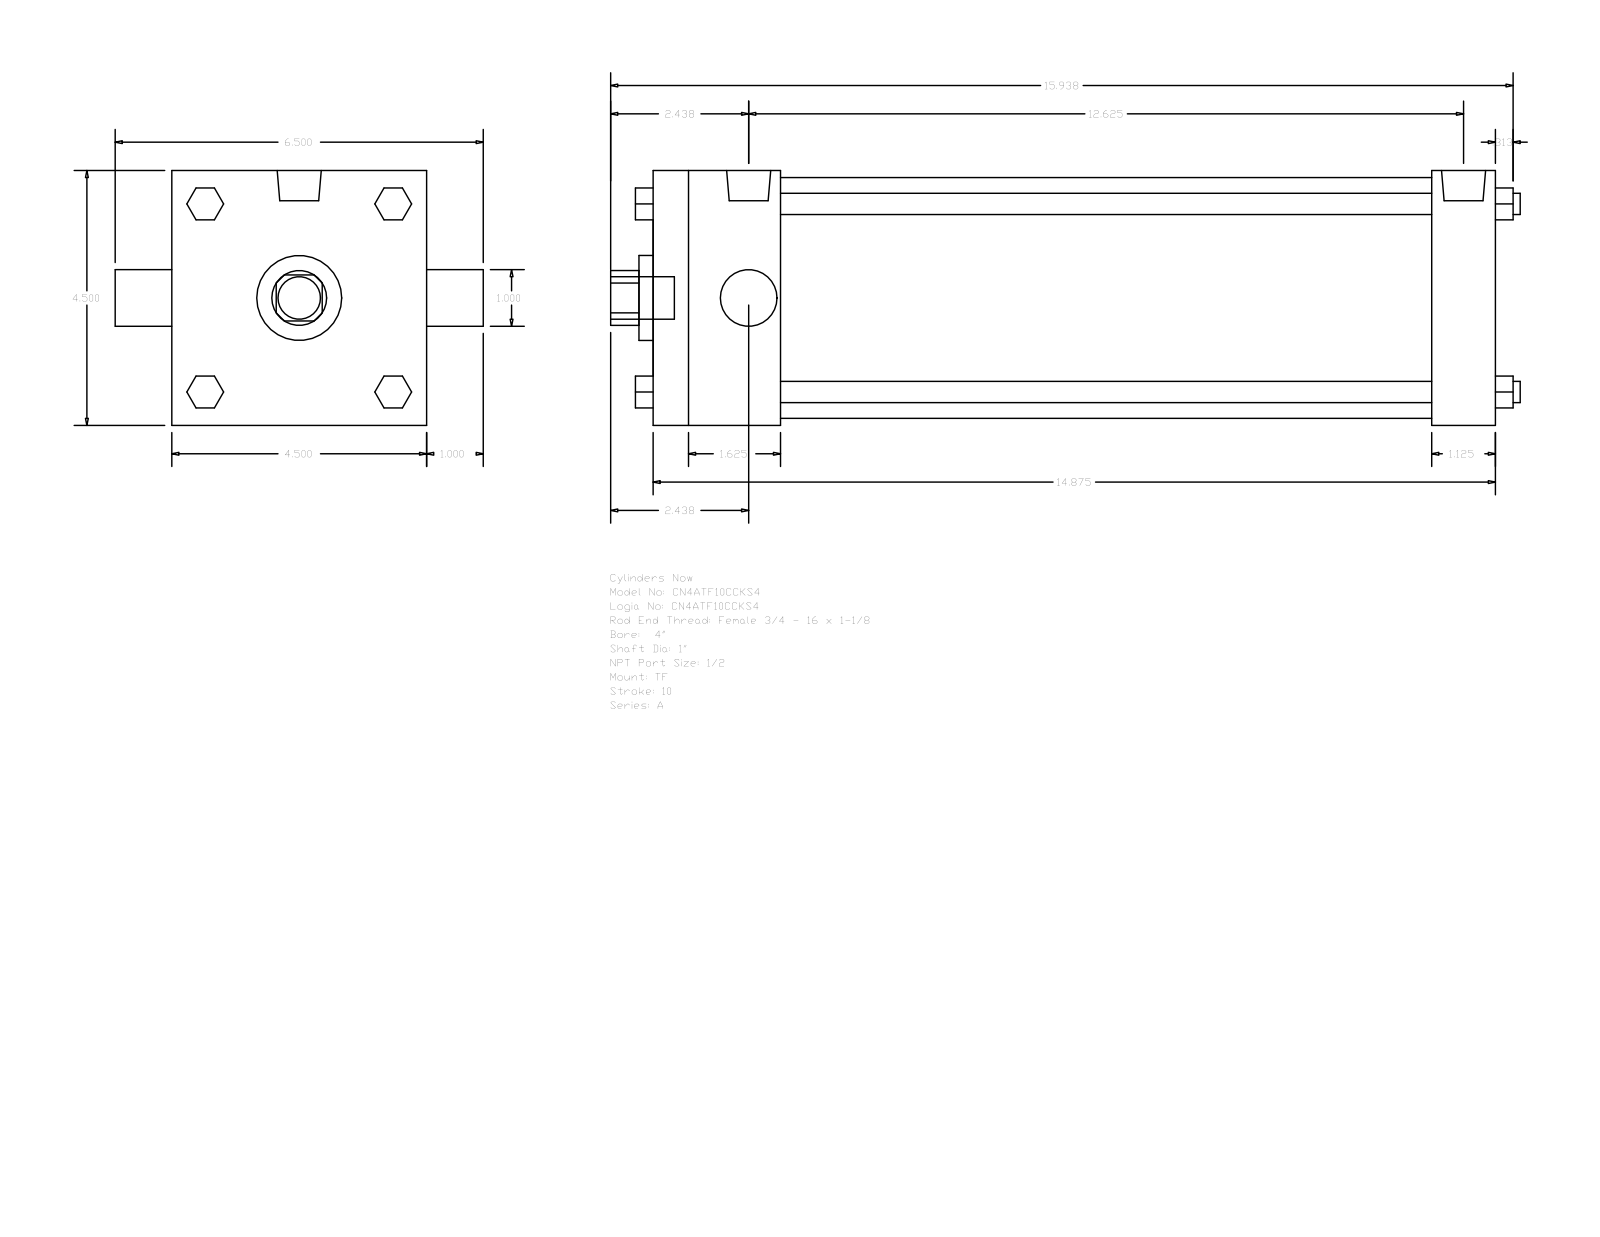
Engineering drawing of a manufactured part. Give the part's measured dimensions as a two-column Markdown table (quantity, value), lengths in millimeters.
| quantity | value |
| --- | --- |
| part name | A_TF__0400_1 |
| STEP written by | GSSL Pune (CONFIG_CONTROL_DESIGN) |
| units | millimeters |
| bodies | 0 solids, 120 faces (92 planar, 28 cylindrical, 0 other) |
| overall size | 407.99 × 165.1 × 114.3 |
| round holes (diameter × count) | 25.4 × 2, 38.1 × 1, 107.95 × 1 |
| round bosses / shafts (diameter × count) | 9.53 × 4, 8.73 × 3, 19.77 × 2, 19.05 × 1 |
| partial cylindrical surfaces (radius × count) | 12.29 × 1 |
| main face-to-face distances | 114.3, 377.83, 349.25, 28.58, 57.15, 292.1, 320.68, 14.29, 42.16, 73.03 |
